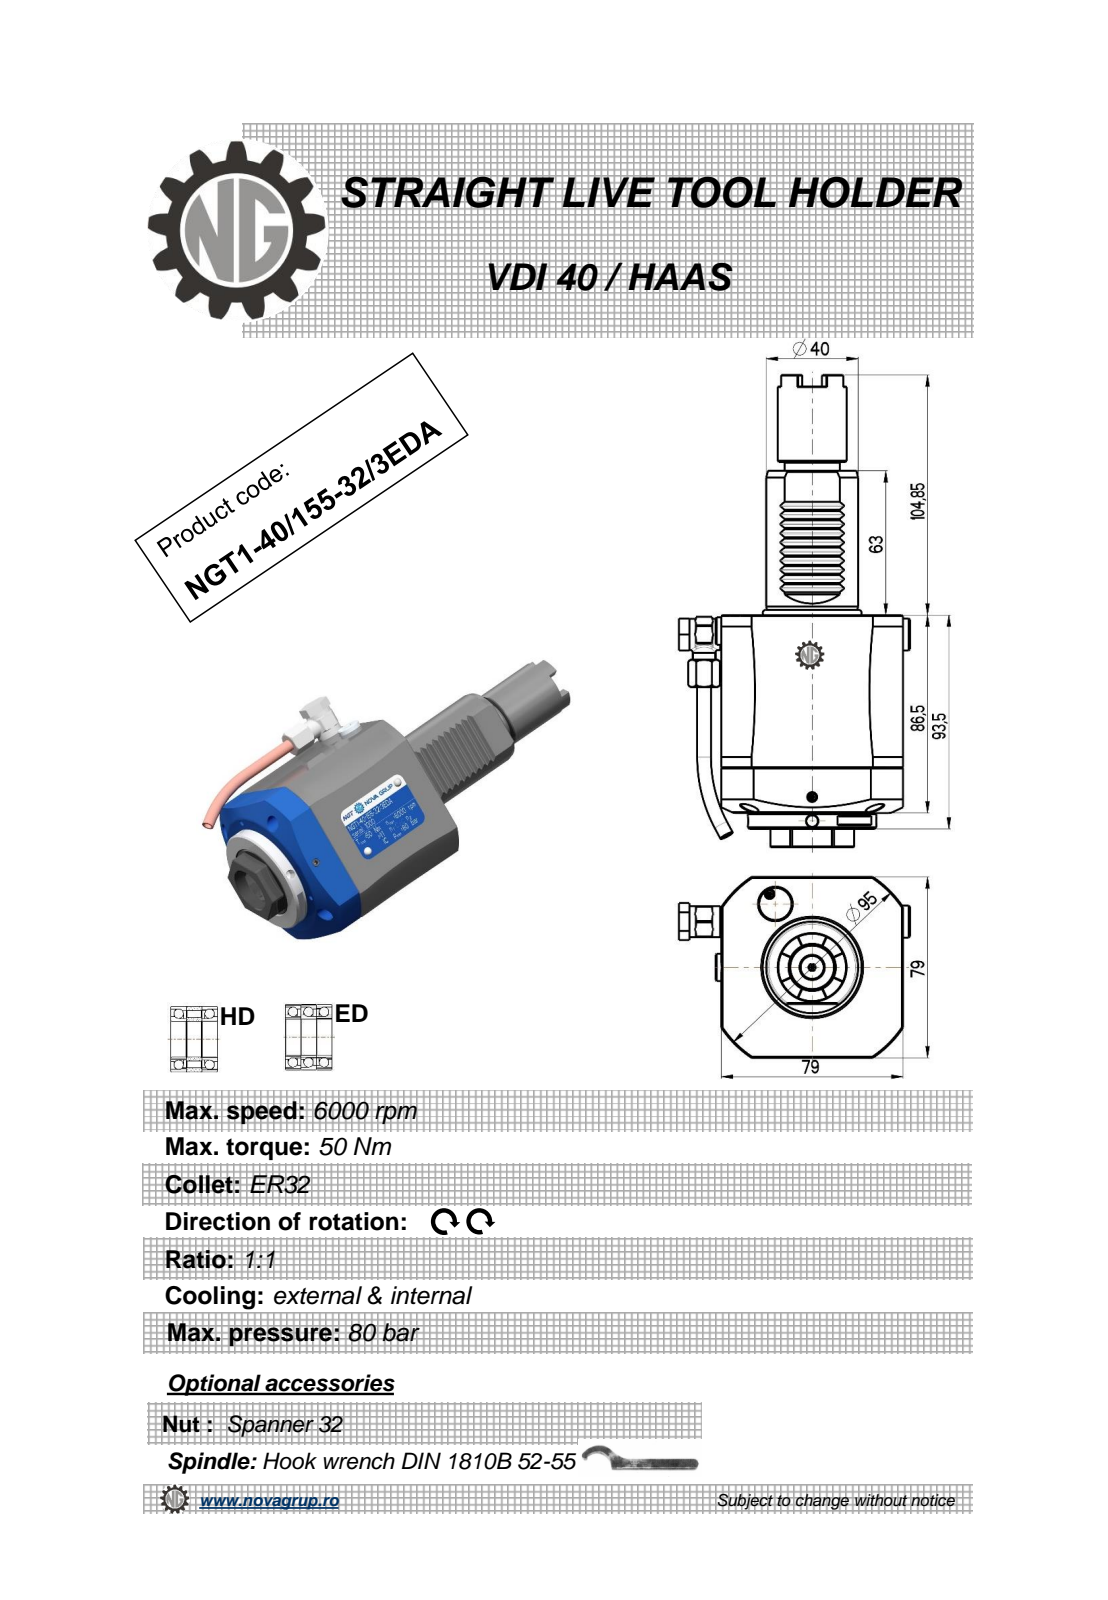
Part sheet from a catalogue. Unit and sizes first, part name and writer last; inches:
Units: inches
Overall size (bounding box): 8.124 × 3.953 × 3.11
Round holes (diameter × count): ⌀0.157 ×3, ⌀0.197 ×2, ⌀0.118 ×1, ⌀0.236 ×1, ⌀0.244 ×1, ⌀0.354 ×1, ⌀0.394 ×1, ⌀0.433 ×1, ⌀0.906 ×1
Round bosses / shafts (diameter × count): ⌀2.205 ×1, ⌀1.575 ×1, ⌀1.181 ×1, ⌀0.945 ×1, ⌀0.551 ×1, ⌀0.535 ×1, ⌀0.512 ×1, ⌀0.472 ×1
Partial cylindrical surfaces — rounded edges, fillets, slot ends (radius × count): R0.012 ×10, R0.016 ×6, R0.02 ×4, R0.303 ×1, R0.394 ×1, R1.85 ×1, R1.87 ×1
Main face-to-face distances: 3.11, 3.406, 0.276, 3.681, 0.111, 0.925, 2.185, 6.161, 5.886, 2.48
Hole centre spacings: 0.016, 2.011, 2.026, 3.304
Volume: 38.25 in³ · Surface area: 90.08 in²
Bodies: 2 solids, 413 faces (181 planar, 103 cylindrical, 129 other)
Part name (STEP PRODUCT): NGT1_40_155_32_3HDA
STEP written by: PRO/ENGINEER BY PARAMETRIC TECHNOLOGY CORPORATION, 2010280 (CONFIG_CONTROL_DESIGN)
